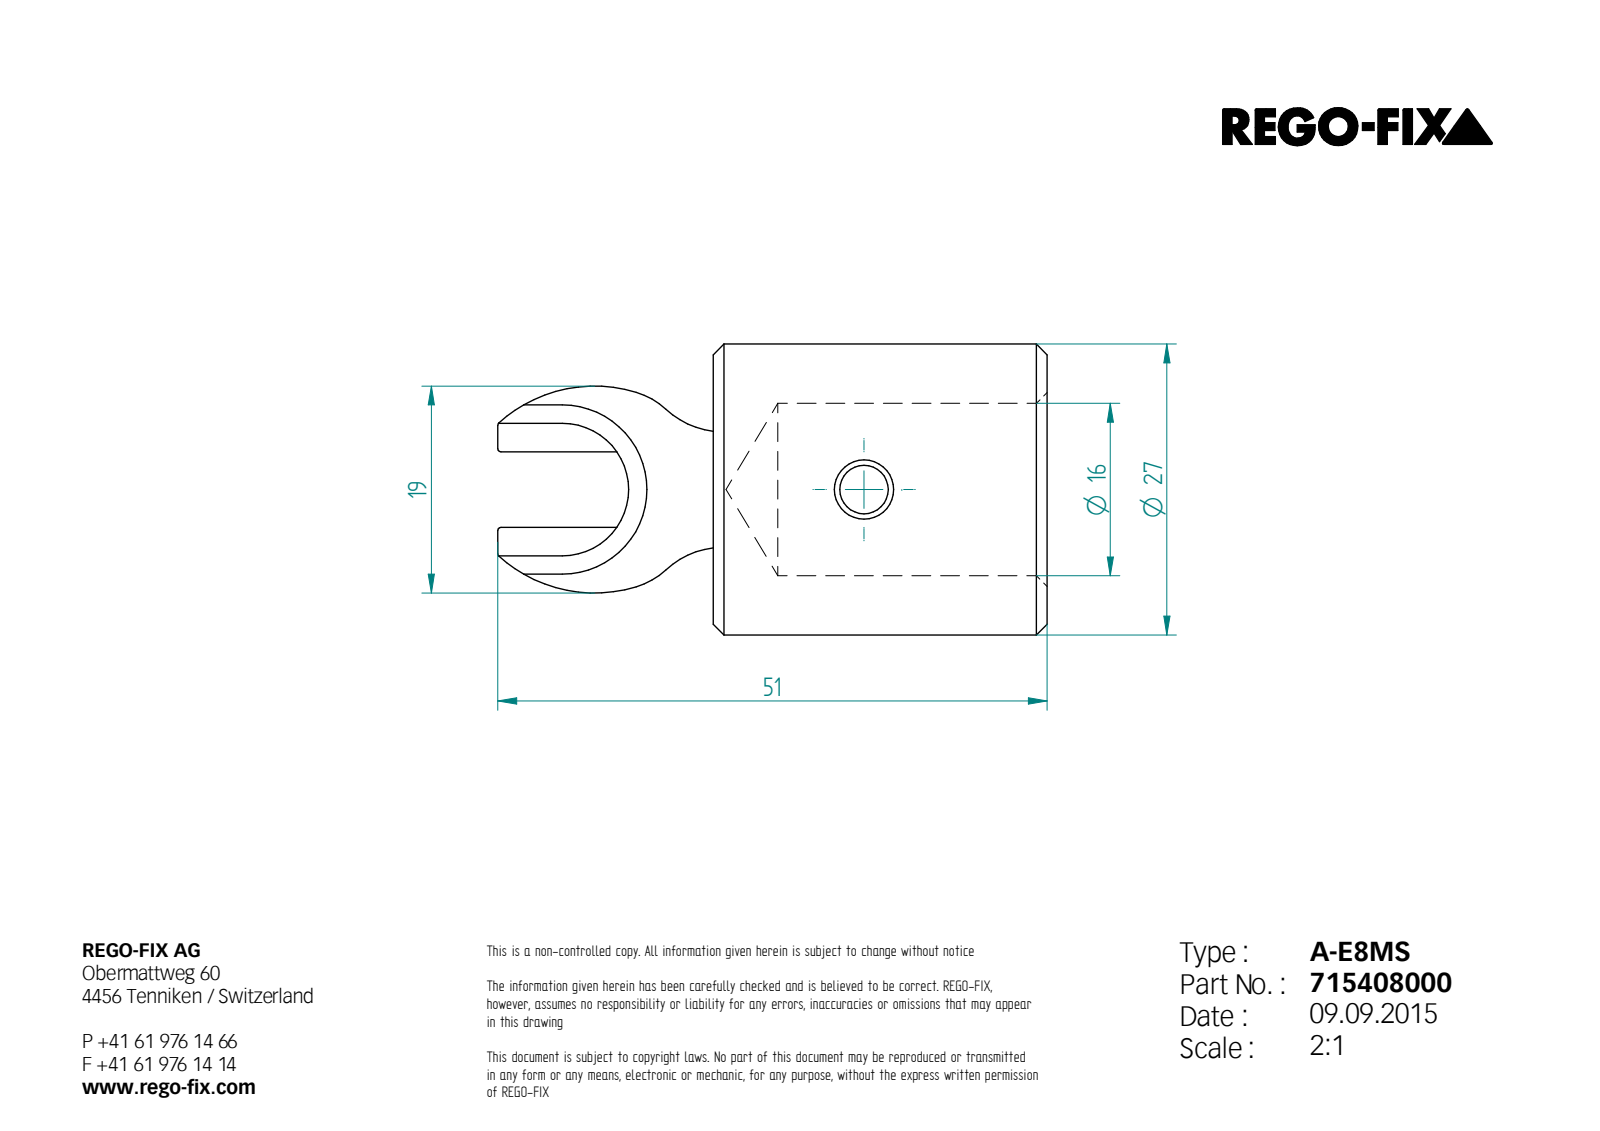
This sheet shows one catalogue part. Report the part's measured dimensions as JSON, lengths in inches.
{"step_written_by": "Unknown (AUTOMOTIVE_DESIGN)", "units": "inches", "bodies": {"solids": 1, "faces": 39, "planar": 16, "cylindrical": 16, "other": 7}, "overall_size": [2.008, 1.063, 1.063], "volume_in3": 0.778, "surface_area_in2": 8.858, "round_holes": [[0.177, 1], [0.217, 1], [0.63, 1]], "round_bosses_or_shafts": [[1.063, 1]], "partial_cylinders_radius": [[0.012, 4], [0.279, 2], [0.315, 2], [0.524, 2], [0.242, 1]], "face_to_face_distances": [1.22, 0.157, 0.067, 0.091, 0.024, 0.326, 0.276, 0.787, 2.008]}
